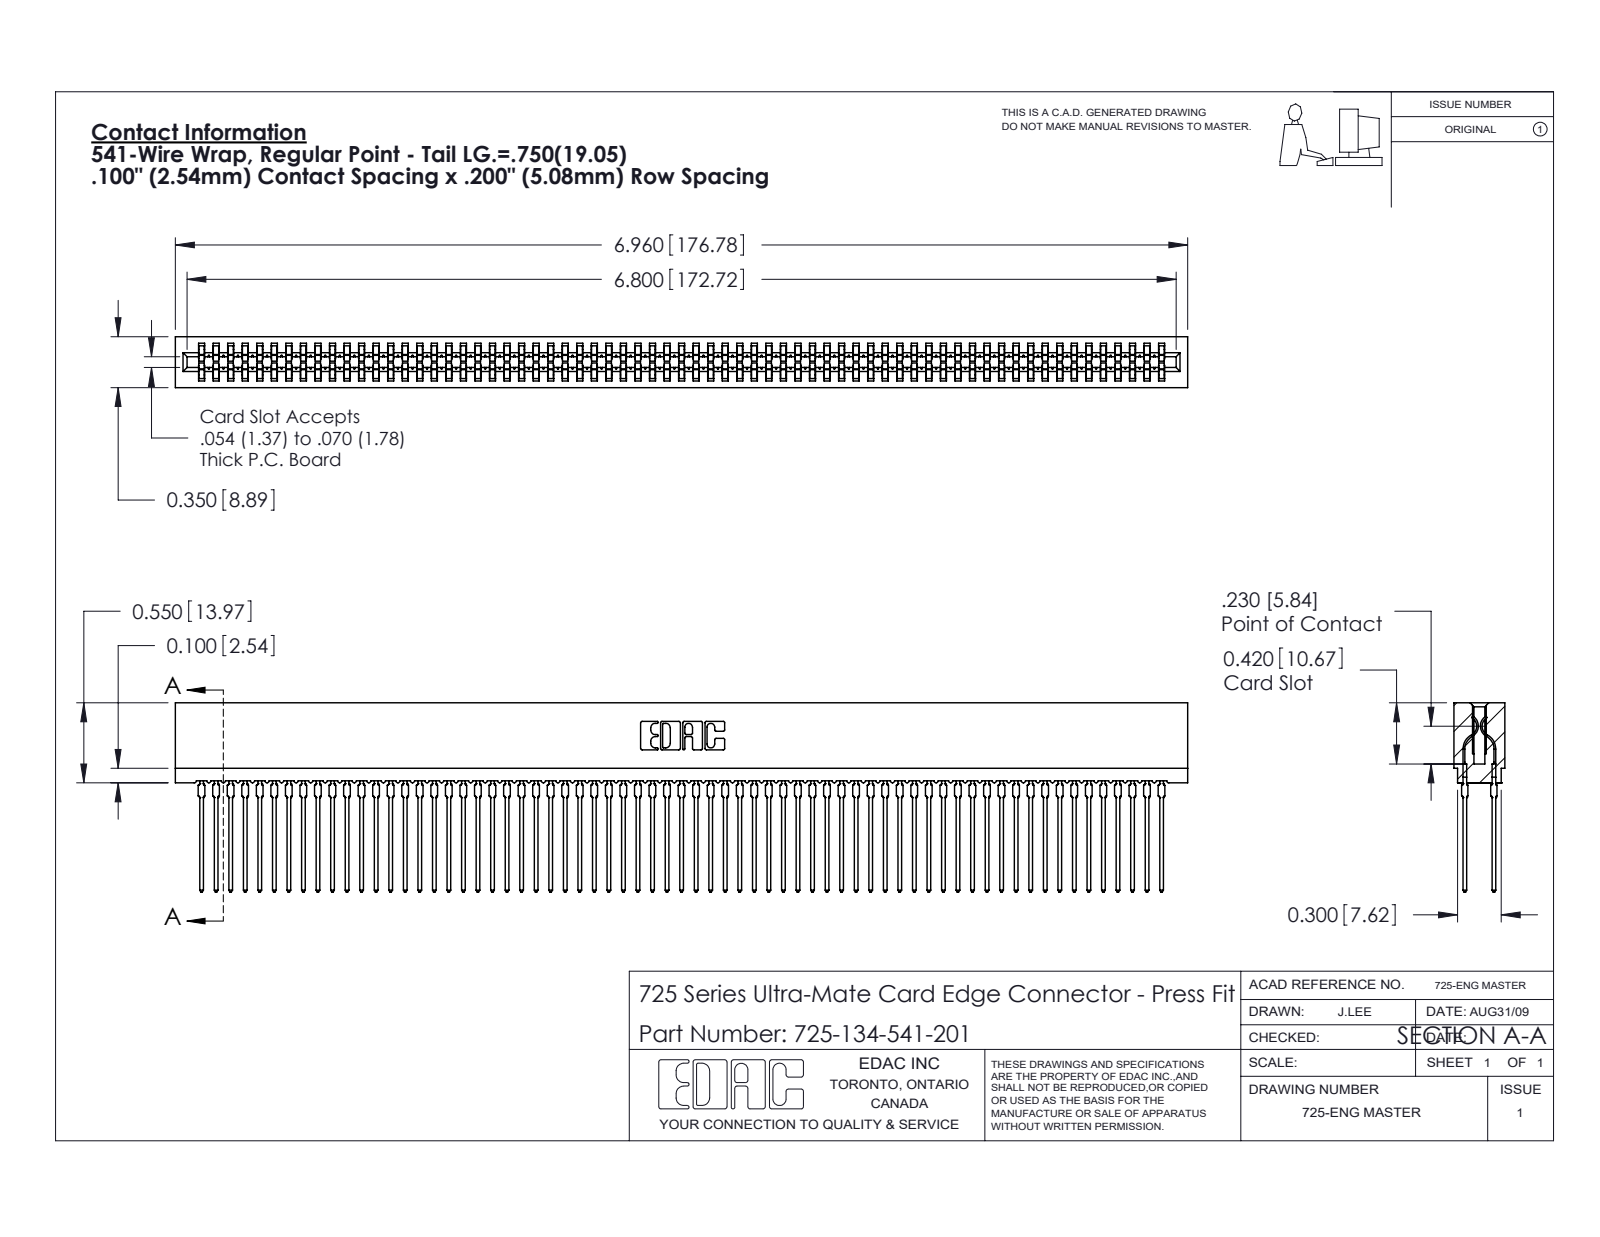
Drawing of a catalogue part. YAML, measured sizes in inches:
part_name: "725-134-541-201; 745-292-001_541; 725 Part_Insulator Option - 01"
step_written_by: "SolidWorks 2020 (CONFIG_CONTROL_DESIGN)"
units: inches
bodies: {solids: 135, faces: 12088, planar: 6219, cylindrical: 2385, other: 3484}
overall_size: [6.96, 1.301, 0.35]
volume: 0.888
surface_area: 52.57
partial_cylinders:
  - {radius: 0.021, count: 268}
  - {radius: 0.015, count: 134}
  - {radius: 0.01, count: 22}
  - {radius: 0.005, count: 8}
  - {radius: 0.011, count: 8}
  - {radius: 0.007, count: 6}
  - {radius: 0.031, count: 6}
  - {radius: 0.026, count: 3}
face_to_face_distances: [0.063, 0.287, 0.2, 0.087, 0.263, 0.025, 0.35, 0.212, 0.138, 0.076]
